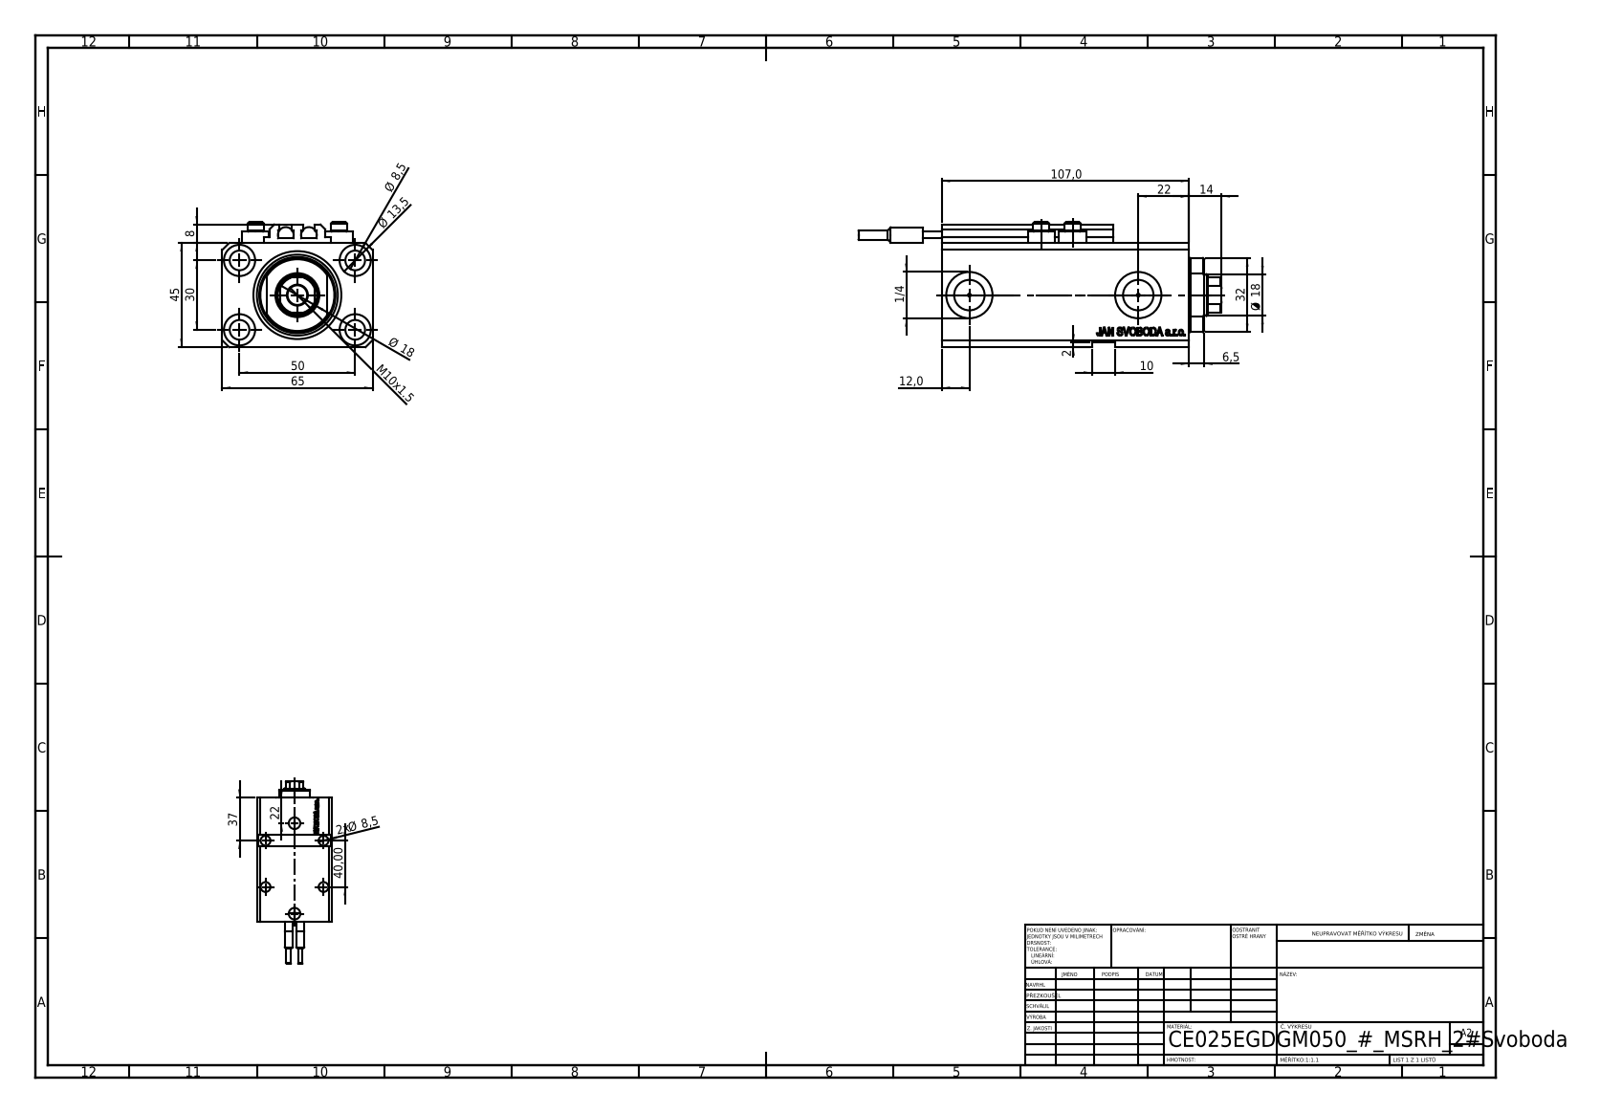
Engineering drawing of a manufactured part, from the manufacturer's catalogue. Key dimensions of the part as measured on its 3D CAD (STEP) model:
Part name (STEP PRODUCT): V250CE_C_VCP; V250CE_VC_E; SWITCH_V250CE; V250CE_E_Body (+1 more)
STEP written by: SolidWorks 2019 (CONFIG_CONTROL_DESIGN)
Units: millimetres
Bodies: 10 solids, 1155 faces (547 planar, 170 cylindrical, 438 other)
Overall size (bounding box): 157 × 65 × 54
Volume: 273 356 mm³ · Surface area: 80 763 mm²
Round holes (diameter × count): ⌀8.5 ×9, ⌀1.25 ×4, ⌀4 ×4, ⌀13.5 ×4, ⌀10 ×2, ⌀13.16 ×2, ⌀20 ×2, ⌀18 ×1, ⌀25 ×1, ⌀38 ×1
Round bosses / shafts (diameter × count): ⌀11.6 ×4, ⌀7 ×4, ⌀6.8 ×2, ⌀6.5 ×2, ⌀4 ×2
Partial cylindrical surfaces — rounded edges, fillets, slot ends (radius × count): R0.2 ×10, R8.5 ×1, R16 ×1
Main face-to-face distances: 45, 65, 2, 47, 93, 3, 14, 107, 10, 5
Hole centre spacings: 29.15, 50, 13.6, 14.76, 15.12, 27.51, 27.89, 30
